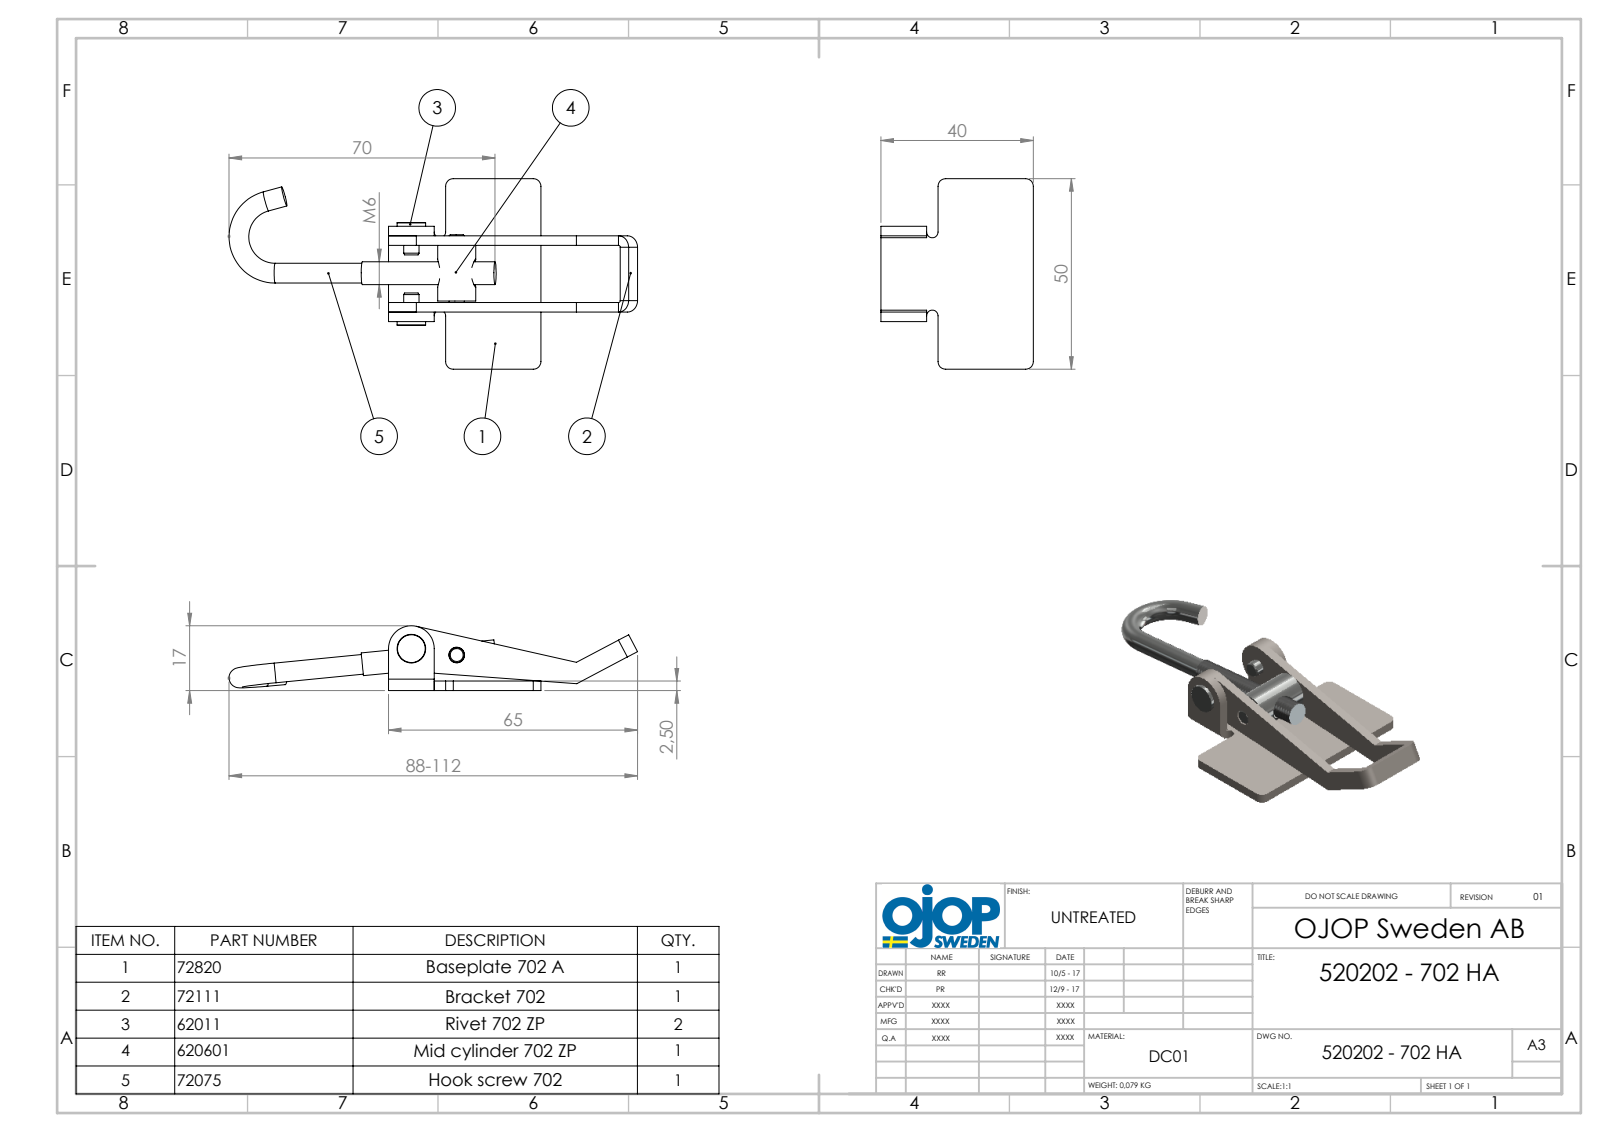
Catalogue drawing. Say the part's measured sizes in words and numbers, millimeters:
The part is named "702 - Bygel; 702 - Hake M6; 702 - Rulle; 702 - A (+2 more)". Its 3-D file was written by "SolidWorks 2015 (AUTOMOTIVE_DESIGN)". It is 6 solids with 132 faces: 57 planar, 57 cylindrical and 18 other. Overall it measures 107.23 by 50 by 17 millimeters. Its volume is 10 863 cubic millimeters and its surface area 10 259 square millimeters. Round holes: 2 of diameter 4.1, 2 of diameter 5. Round bosses or shafts: 2 of diameter 6, 2 of diameter 5.18, 2 of diameter 4, 1 of diameter 10, 1 of diameter 7.5. Partial cylindrical surfaces (rounded edges, fillets, slot ends): 4 of radius 0.5, 4 of radius 2, 4 of radius 3, 2 of radius 1.5, 1 of radius 6. The main face-to-face distances are 2.5, 17.5, 20, 15, 5, 22.5, 25, 12.5, 32.5, 35. The hole center spacings are 12.03.
